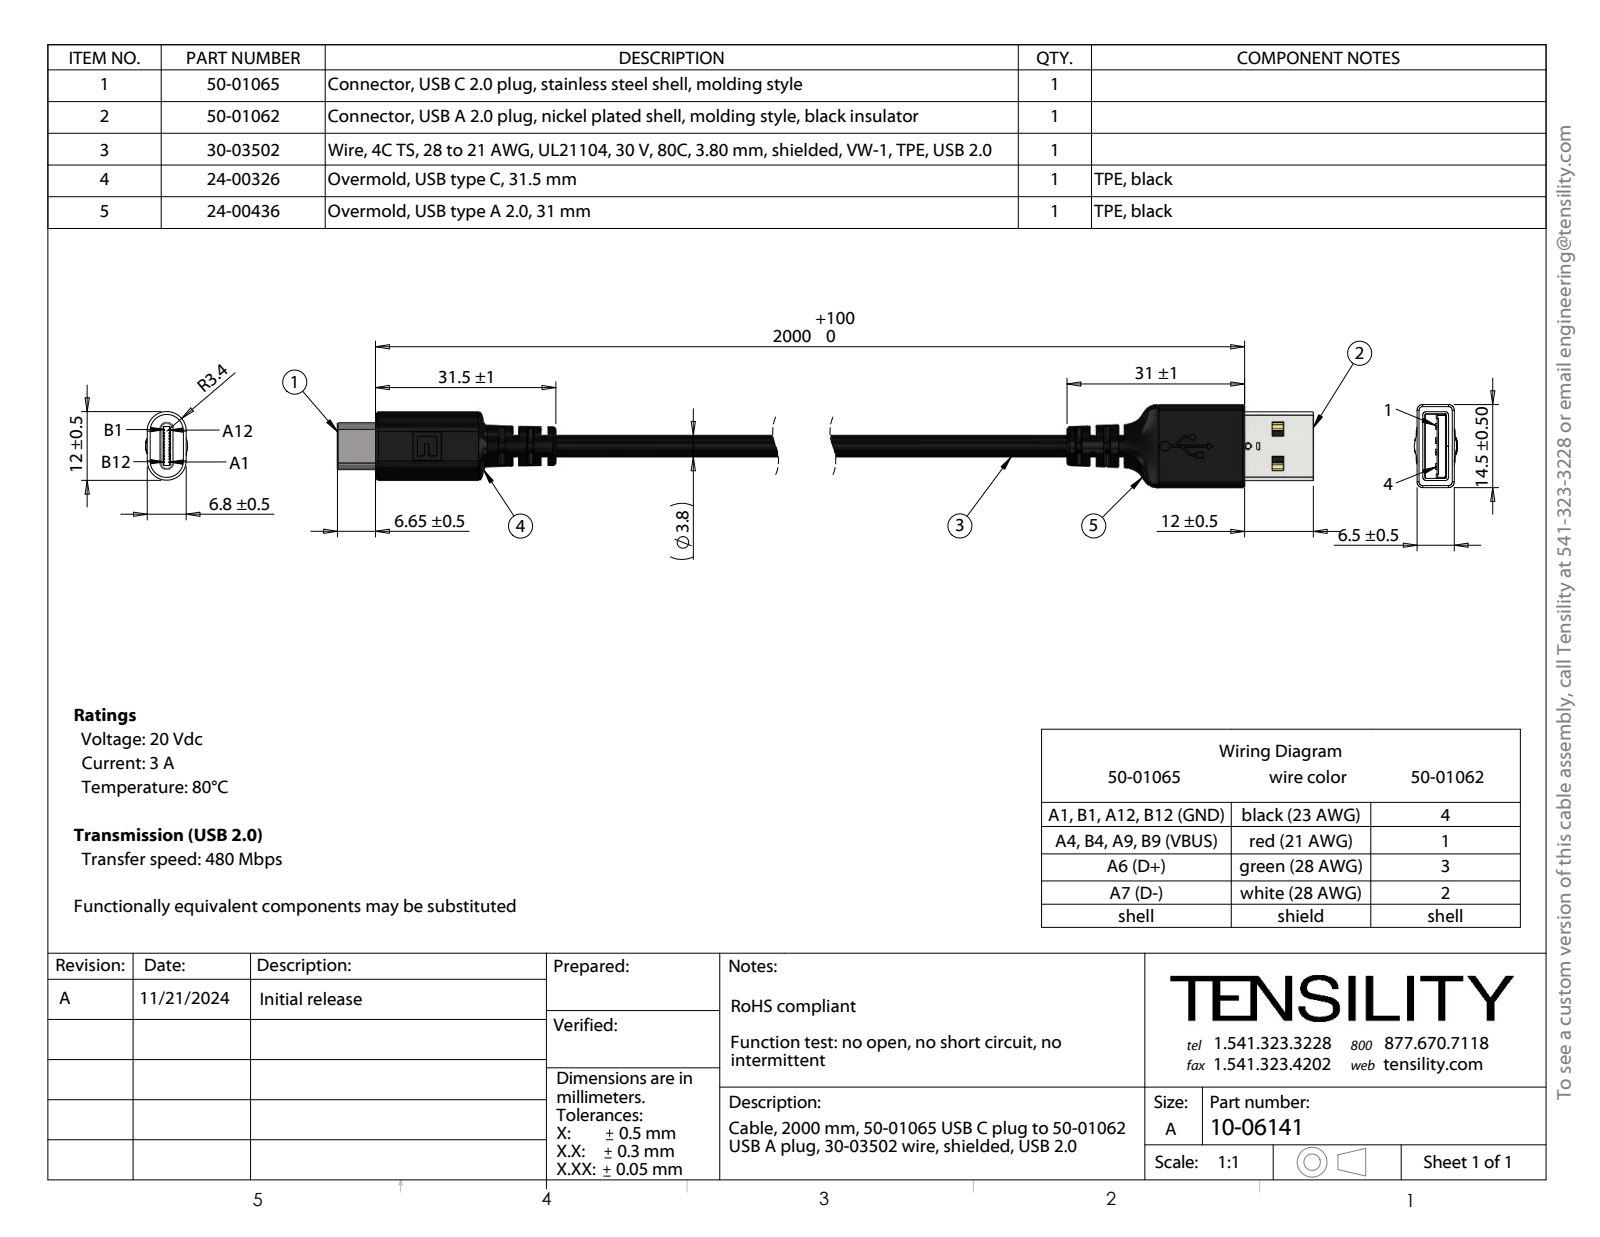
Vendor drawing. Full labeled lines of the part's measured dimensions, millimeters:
Part name (STEP PRODUCT): 24-00326; 50-01062_shell2; 50-01062_crimp_Assembled; 24-00436 (+8 more)
STEP written by: SolidWorks 2021 (CONFIG_CONTROL_DESIGN)
Units: millimetres
Bodies: 125 solids, 1970 faces (1014 planar, 630 cylindrical, 326 other)
Overall size (bounding box): 200.15 × 14.5 × 7.54
Volume: 5 918 mm³ · Surface area: 22 580 mm²
Round holes (diameter × count): ⌀1.04 ×1, ⌀1.74 ×1, ⌀2.61 ×1, ⌀2.64 ×1, ⌀2.84 ×1
Round bosses / shafts (diameter × count): ⌀0.83 ×2, ⌀3.8 ×1, ⌀2.63 ×1, ⌀1.2 ×1, ⌀1 ×1
Partial cylindrical surfaces — rounded edges, fillets, slot ends (radius × count): R0.25 ×40, R0.2 ×34, R0.5 ×32, R0.35 ×14, R0.4 ×14, R0.3 ×13, R0.31 ×5, R0.6 ×5
Main face-to-face distances: 0.35, 4.15, 1, 5.5, 1.35, 5.15, 1.5, 2.5, 4.5, 3.8
Hole centre spacings: 5.12
